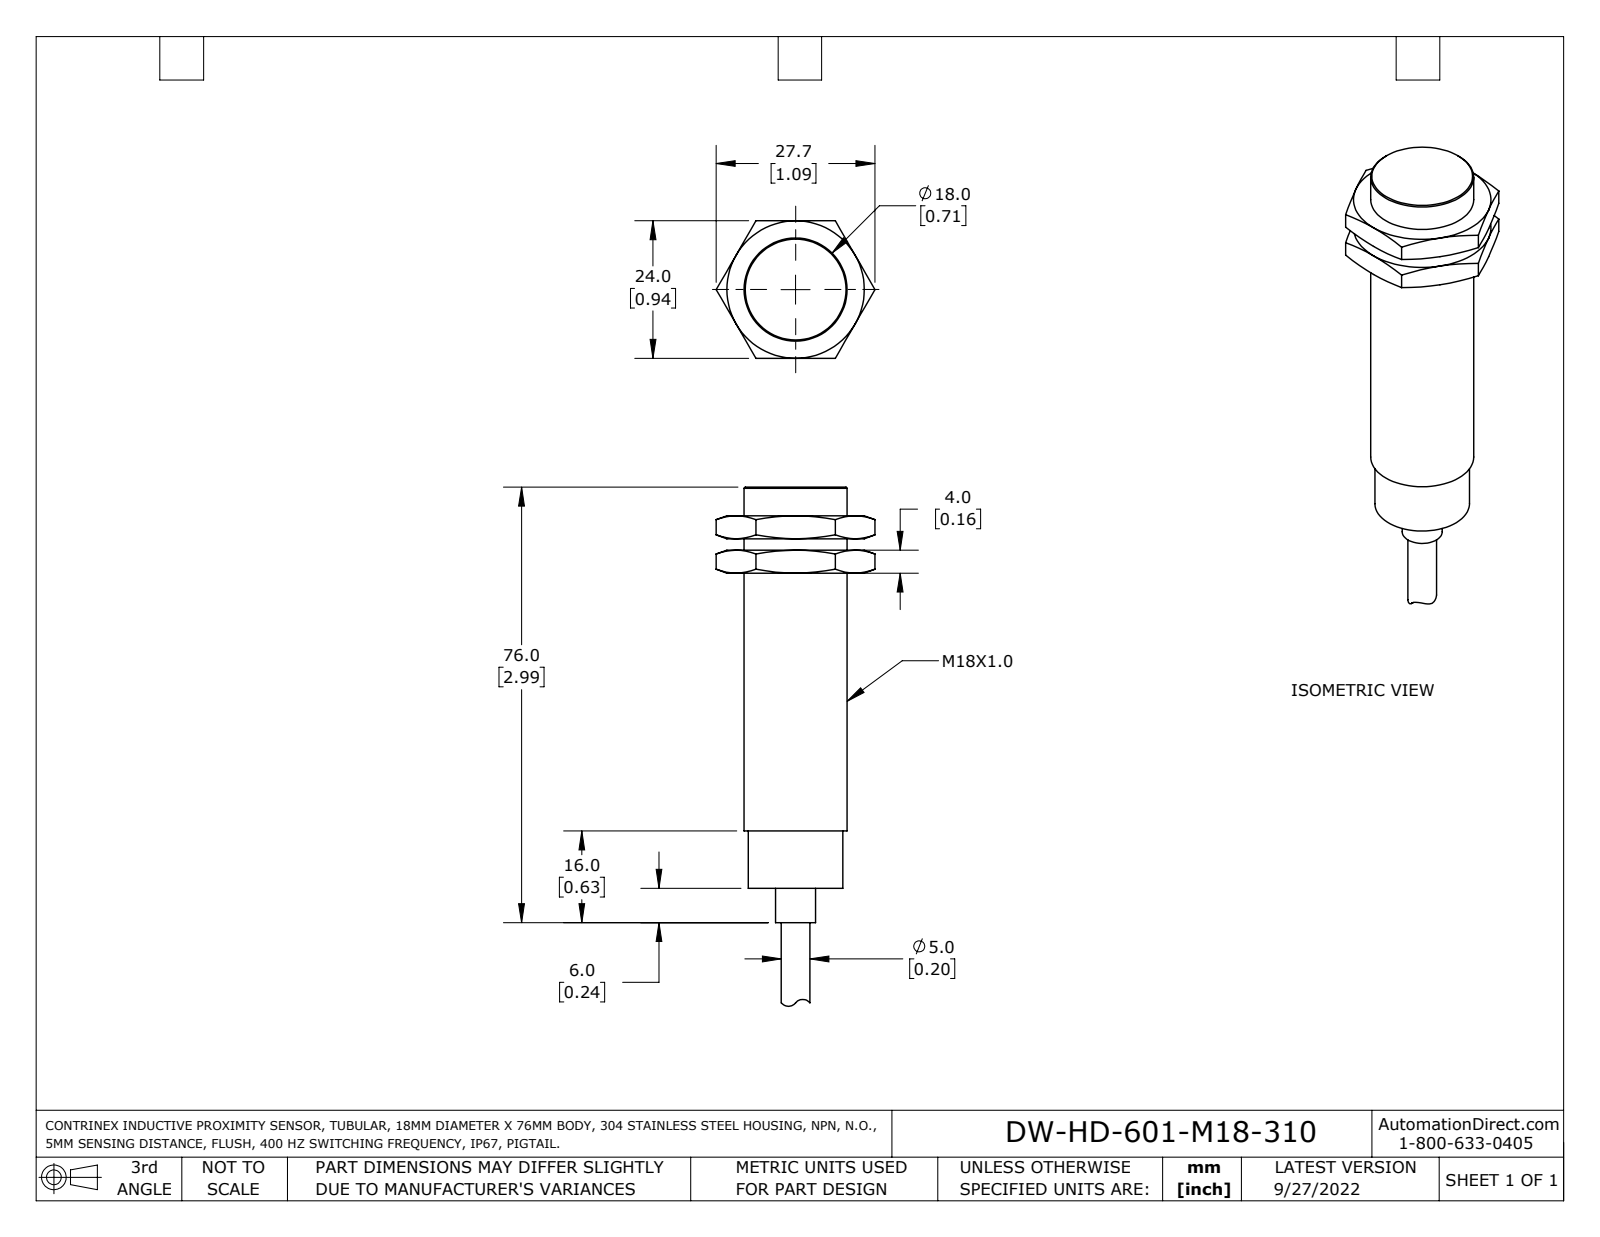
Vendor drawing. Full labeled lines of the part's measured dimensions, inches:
Part name (STEP PRODUCT): DW-HD-601-M18-310
STEP written by: SolidWorks 2021 (AUTOMOTIVE_DESIGN)
Units: inches
Bodies: 1 solid, 53 faces (20 planar, 8 cylindrical, 25 other)
Overall size (bounding box): 3.567 × 1.091 × 0.945
Volume: 1.21 in³ · Surface area: 9.134 in²
Round bosses / shafts (diameter × count): ⌀0.709 ×1, ⌀0.65 ×1, ⌀0.276 ×1, ⌀0.197 ×1
Partial cylindrical surfaces — rounded edges, fillets, slot ends (radius × count): R0.063 ×2
Main face-to-face distances: 0.236, 0.157, 0.945, 0.394, 2.165, 0.197, 0.433, 0.354, 0.079, 0.591
